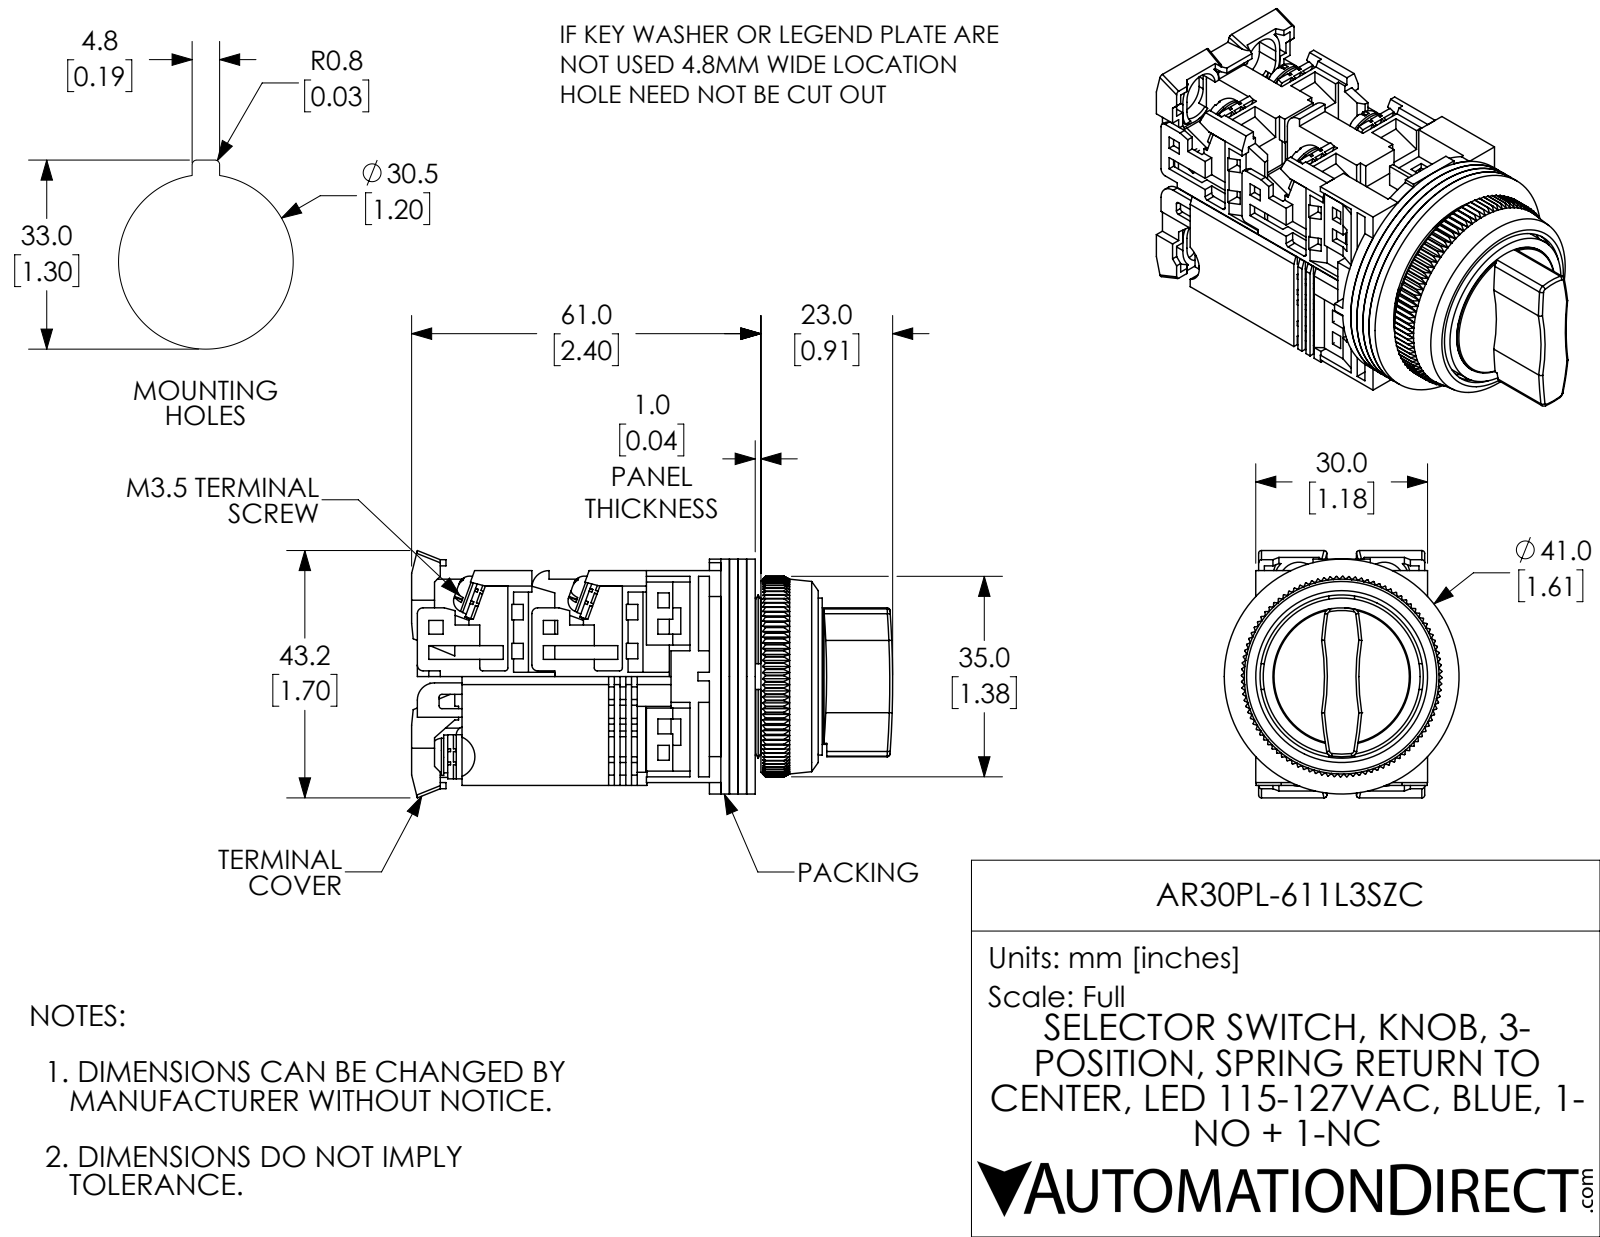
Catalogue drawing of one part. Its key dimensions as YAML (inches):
part_name: "AR30PL-611L3SZC"
step_written_by: "SolidWorks 2017 (AUTOMOTIVE_DESIGN)"
units: inches
bodies: {solids: 34, faces: 2724, planar: 2033, cylindrical: 354, other: 337}
overall_size: [3.307, 1.7, 1.614]
volume: 3.442
surface_area: 70.72
round_holes:
  - {diameter: 0.138, count: 8}
  - {diameter: 0.142, count: 6}
  - {diameter: 0.118, count: 3}
  - {diameter: 0.472, count: 1}
  - {diameter: 0.709, count: 1}
  - {diameter: 0.768, count: 1}
  - {diameter: 0.827, count: 1}
  - {diameter: 1.122, count: 1}
  - {diameter: 1.181, count: 1}
  - {diameter: 1.252, count: 1}
round_bosses_or_shafts:
  - {diameter: 0.26, count: 6}
  - {diameter: 0.138, count: 4}
  - {diameter: 0.063, count: 2}
  - {diameter: 1.614, count: 1}
  - {diameter: 1.15, count: 1}
  - {diameter: 1.079, count: 1}
  - {diameter: 0.945, count: 1}
  - {diameter: 0.886, count: 1}
partial_cylinders:
  - {radius: 0.059, count: 25}
  - {radius: 0.02, count: 15}
  - {radius: 0.039, count: 8}
  - {radius: 0.138, count: 4}
  - {radius: 0.177, count: 4}
  - {radius: 0.118, count: 3}
  - {radius: 1.575, count: 2}
  - {radius: 2.953, count: 2}
face_to_face_distances: [0.059, 0.118, 0.177, 0.039, 0.748, 0.079, 0.787, 0.063, 0.689, 0.197]
hole_center_spacings: [0.579, 0.269, 0.638, 0.297, 0.624, 0.02, 0.302, 0.583]
